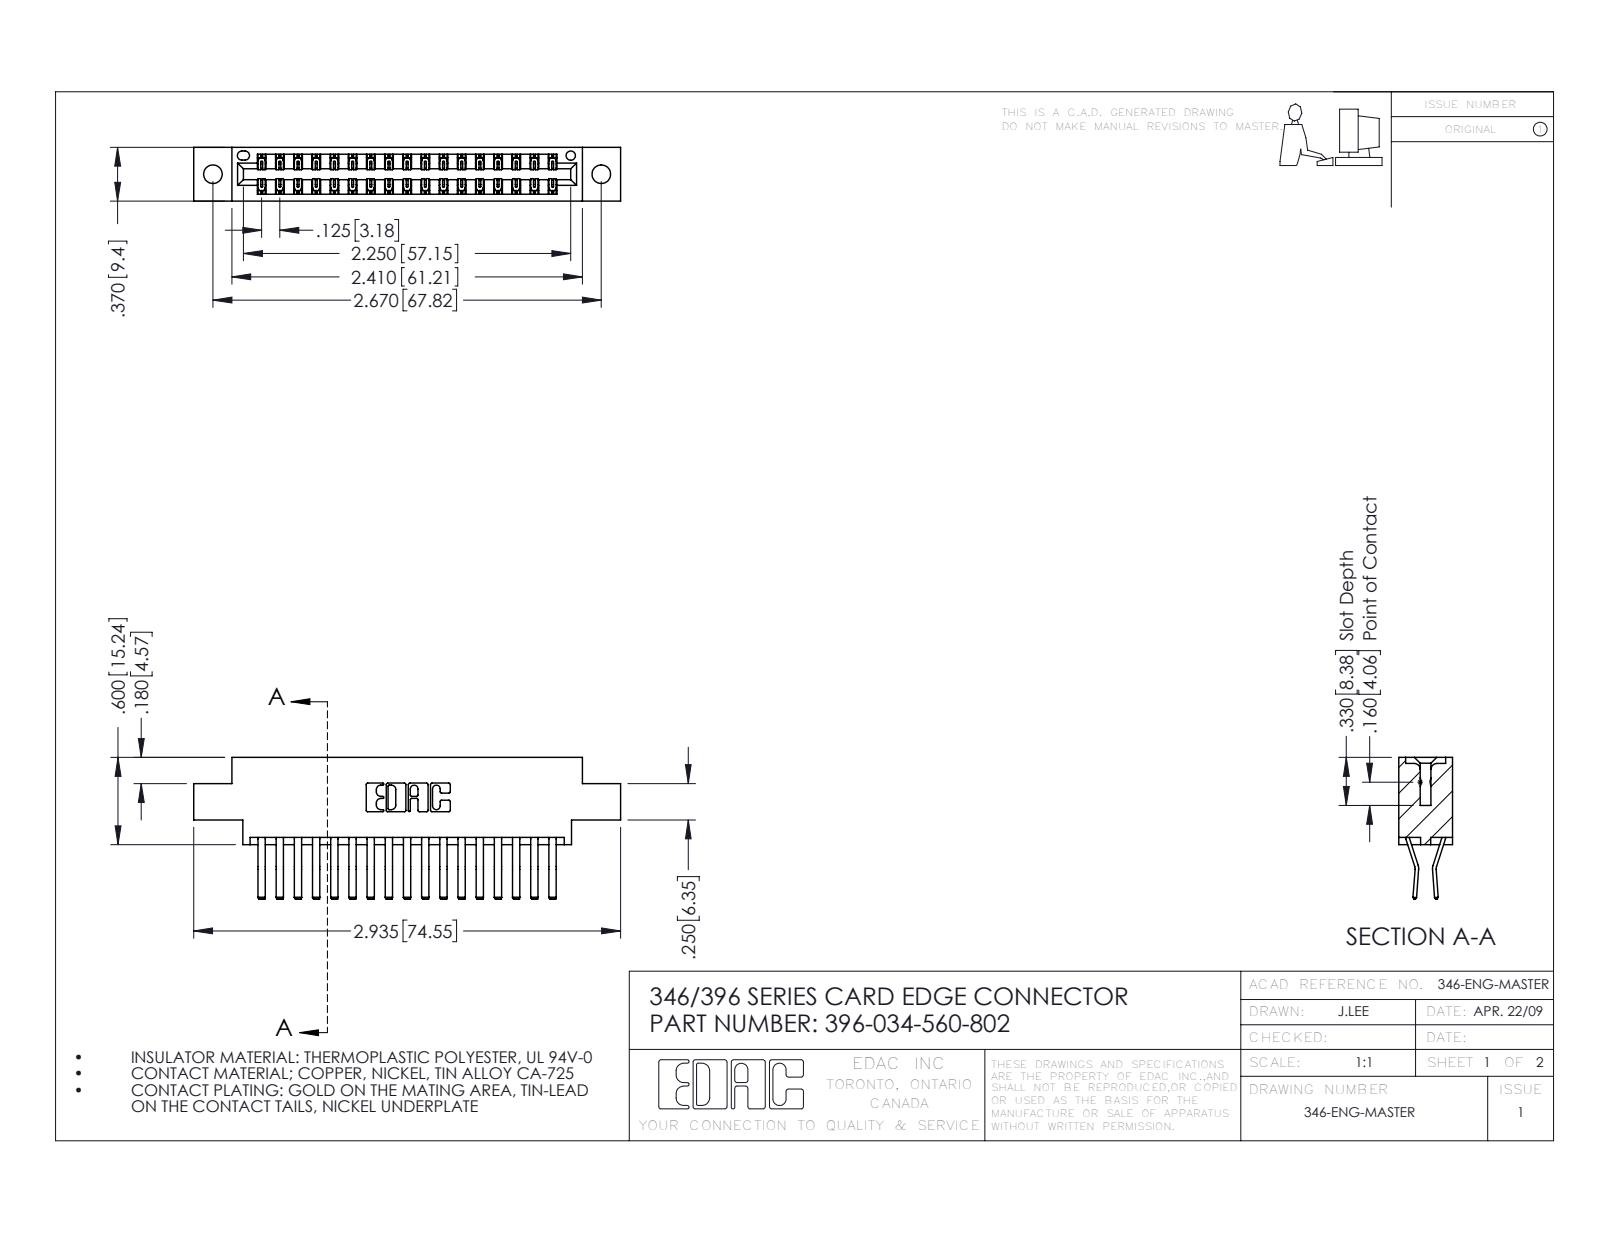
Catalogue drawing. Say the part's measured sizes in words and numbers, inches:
The part is named "396-034-560-802; 345-292-001_560 Tail; 346 Part_0.170 Offset - 0.128 Dia". Its 3-D file was written by "SolidWorks 2016 (CONFIG_CONTROL_DESIGN)". It is 35 solids with 1962 faces: 1270 planar, 692 cylindrical and 0 other. Overall it measures 2.935 by 0.975 by 0.37 inches. Its volume is 0.434 cubic inches and its surface area 15.32 square inches. Round holes: 2 of diameter 0.128, 1 of diameter 0.064. Partial cylindrical surfaces (rounded edges, fillets, slot ends): 51 of radius 0.006, 22 of radius 0.01, 6 of radius 0.007, 6 of radius 0.031, 3 of radius 0.026, 2 of radius 0.01, 2 of radius 0.014, 2 of radius 0.022. The main face-to-face distances are 0.048, 0.322, 0.37, 0.25, 0.025, 0.072, 0.298, 0.275, 0.148, 0.222. The hole center spacings are 0.246, 2.463, 2.67.
